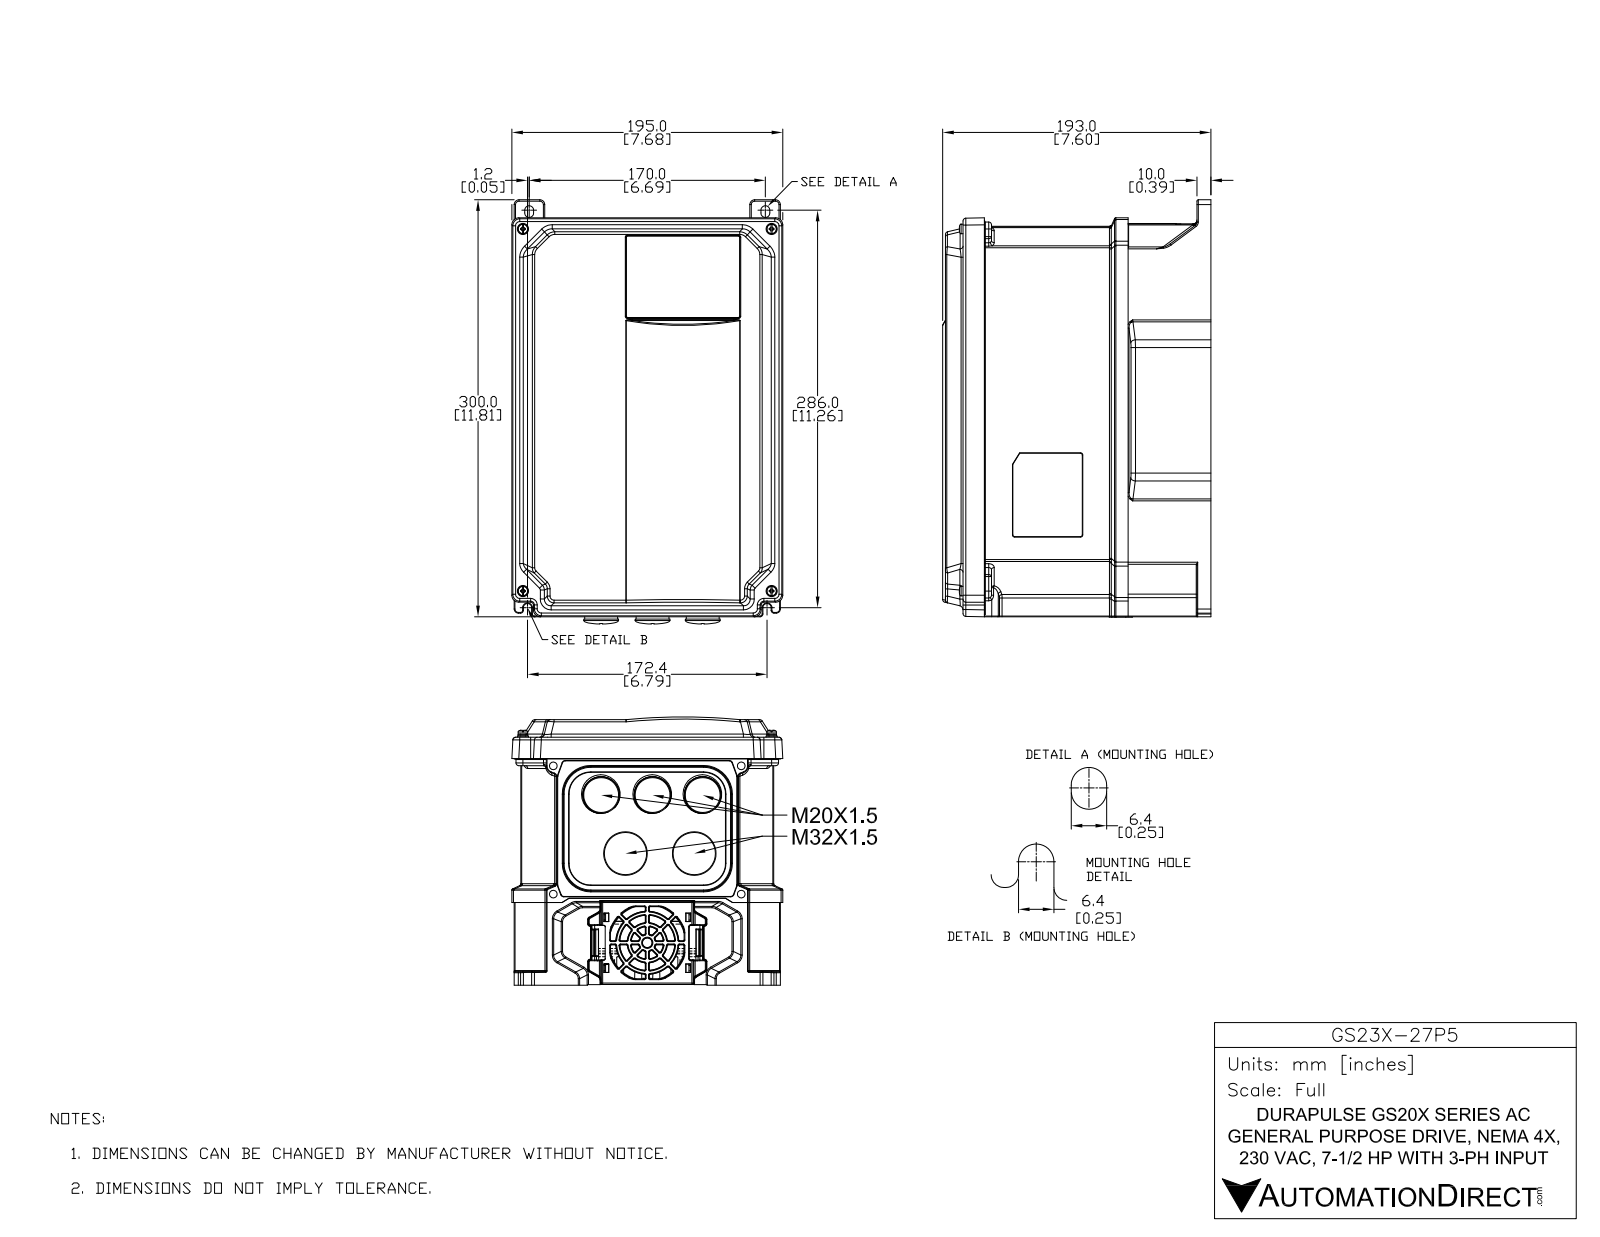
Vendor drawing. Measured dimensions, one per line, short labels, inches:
name: VFD-MS300-NEMA4X-C-PD-3D00 red 2 R1 wo CASE with wo LID Rr2 COMPL 1 EX 1 Coord 1 fXT
written by: SolidWorks 2017 (AUTOMOTIVE_DESIGN)
unit: in
bodies: 18 solids, 3366 faces (1339 planar, 898 cylindrical, 1129 other)
size: 12.016 × 7.69 × 7.677
volume: 102.7 in³; area: 1 139 in²
holes: 4× ⌀0.157, 4× ⌀0.217, 3× ⌀0.591, 3× ⌀0.724, 2× ⌀1.197, 1× ⌀2.165
bosses: 3× ⌀0.988, 3× ⌀0.929, 3× ⌀0.78, 1× ⌀1.575
rounds: 181× R0.02, 150× R0.012, 124× R0.039, 43× R0.079, 37× R0.118, 28× R0.197, 20× R0.236, 14× R0.126
face distances: 0.039, 6.861, 6.9, 0.15, 0.35, 7.55, 7.511, 0.65, 0.234, 7.05
hole spacings: 1.392, 1.969, 2.784, 7.047, 10.255, 12.443, 1.421, 1.457
